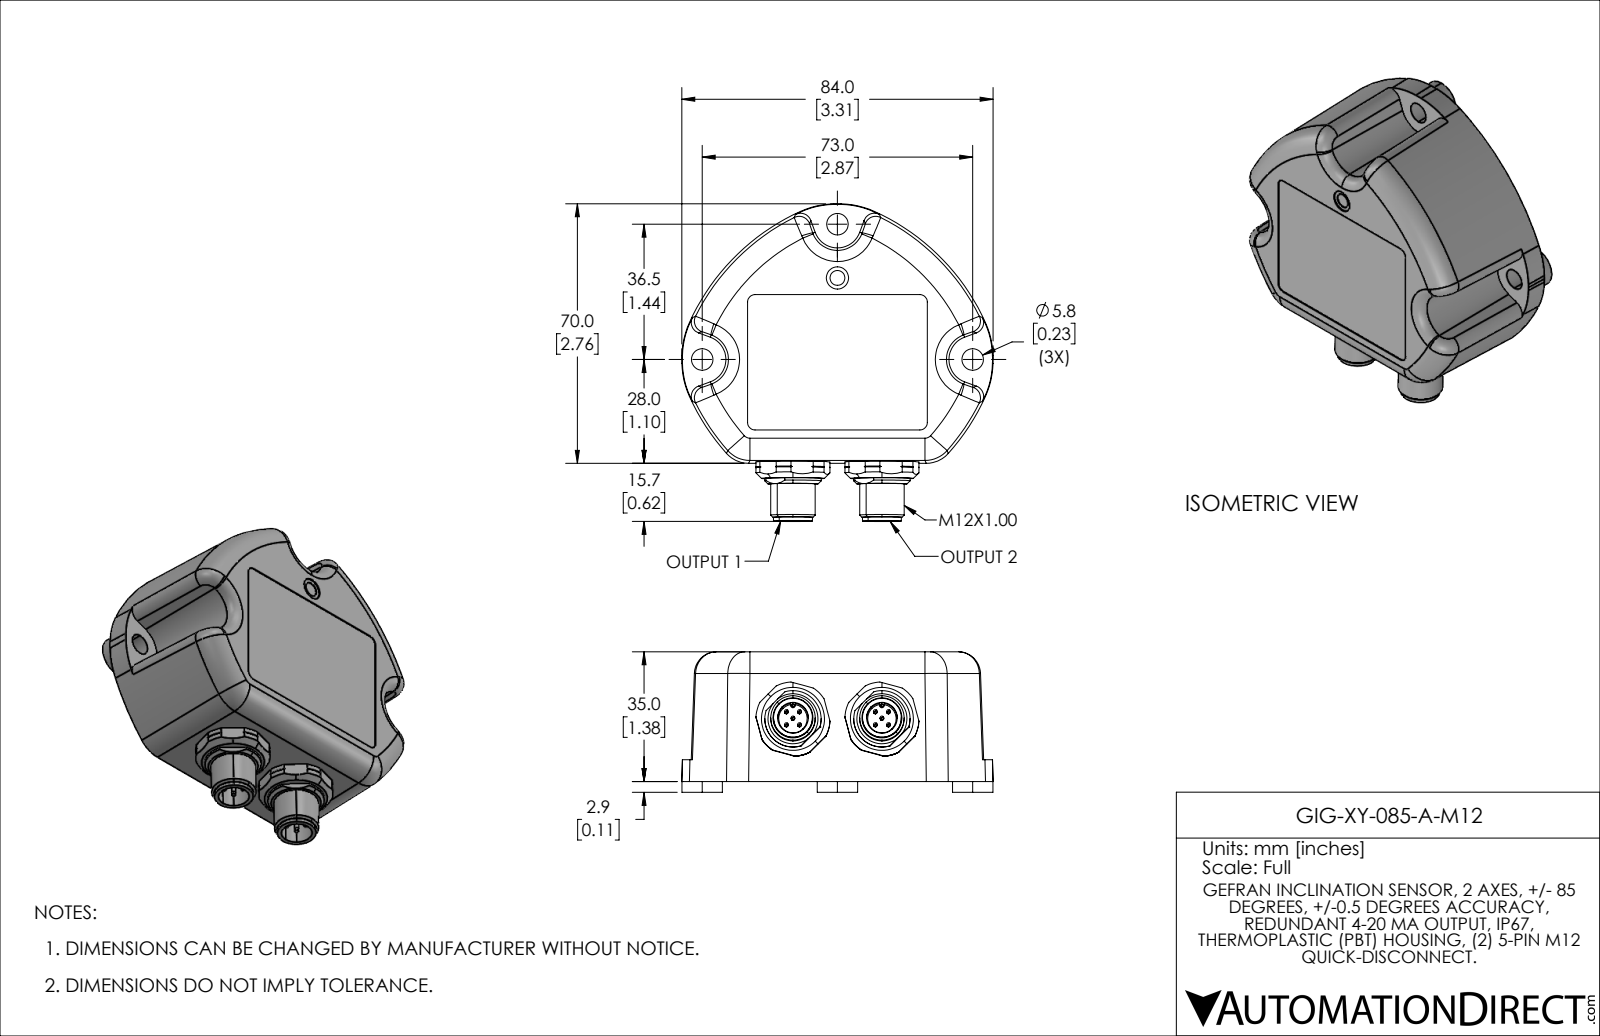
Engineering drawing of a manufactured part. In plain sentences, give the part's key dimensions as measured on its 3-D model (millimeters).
The part is named "GIG-XY-085-A-M12". Its 3-D file was written by "SolidWorks 2021 (AUTOMOTIVE_DESIGN)". It is 1 solid with 365 faces: 87 planar, 123 cylindrical and 155 other. Overall it measures 85.7 by 84 by 37.9 millimeters. Its volume is 148 000 cubic millimeters and its surface area 20 890 square millimeters. Round holes: 3 of diameter 5.8, 2 of diameter 8.3, 1 of diameter 4, 1 of diameter 6. Round bosses or shafts: 10 of diameter 1, 3 of diameter 10.9, 2 of diameter 12, 2 of diameter 10.5. Partial cylindrical surfaces (rounded edges, fillets, slot ends): 4 of radius 0.5, 4 of radius 2, 3 of radius 7.6, 2 of radius 0.6, 2 of radius 6.9, 2 of radius 10, 1 of radius 6, 1 of radius 7.6. The main face-to-face distances are 34.8, 35, 5.9, 28.9, 29.1, 2.9, 8.8, 37.7, 37.9, 17. The hole center spacings are 42.6, 51.6, 14.5, 24, 73.
